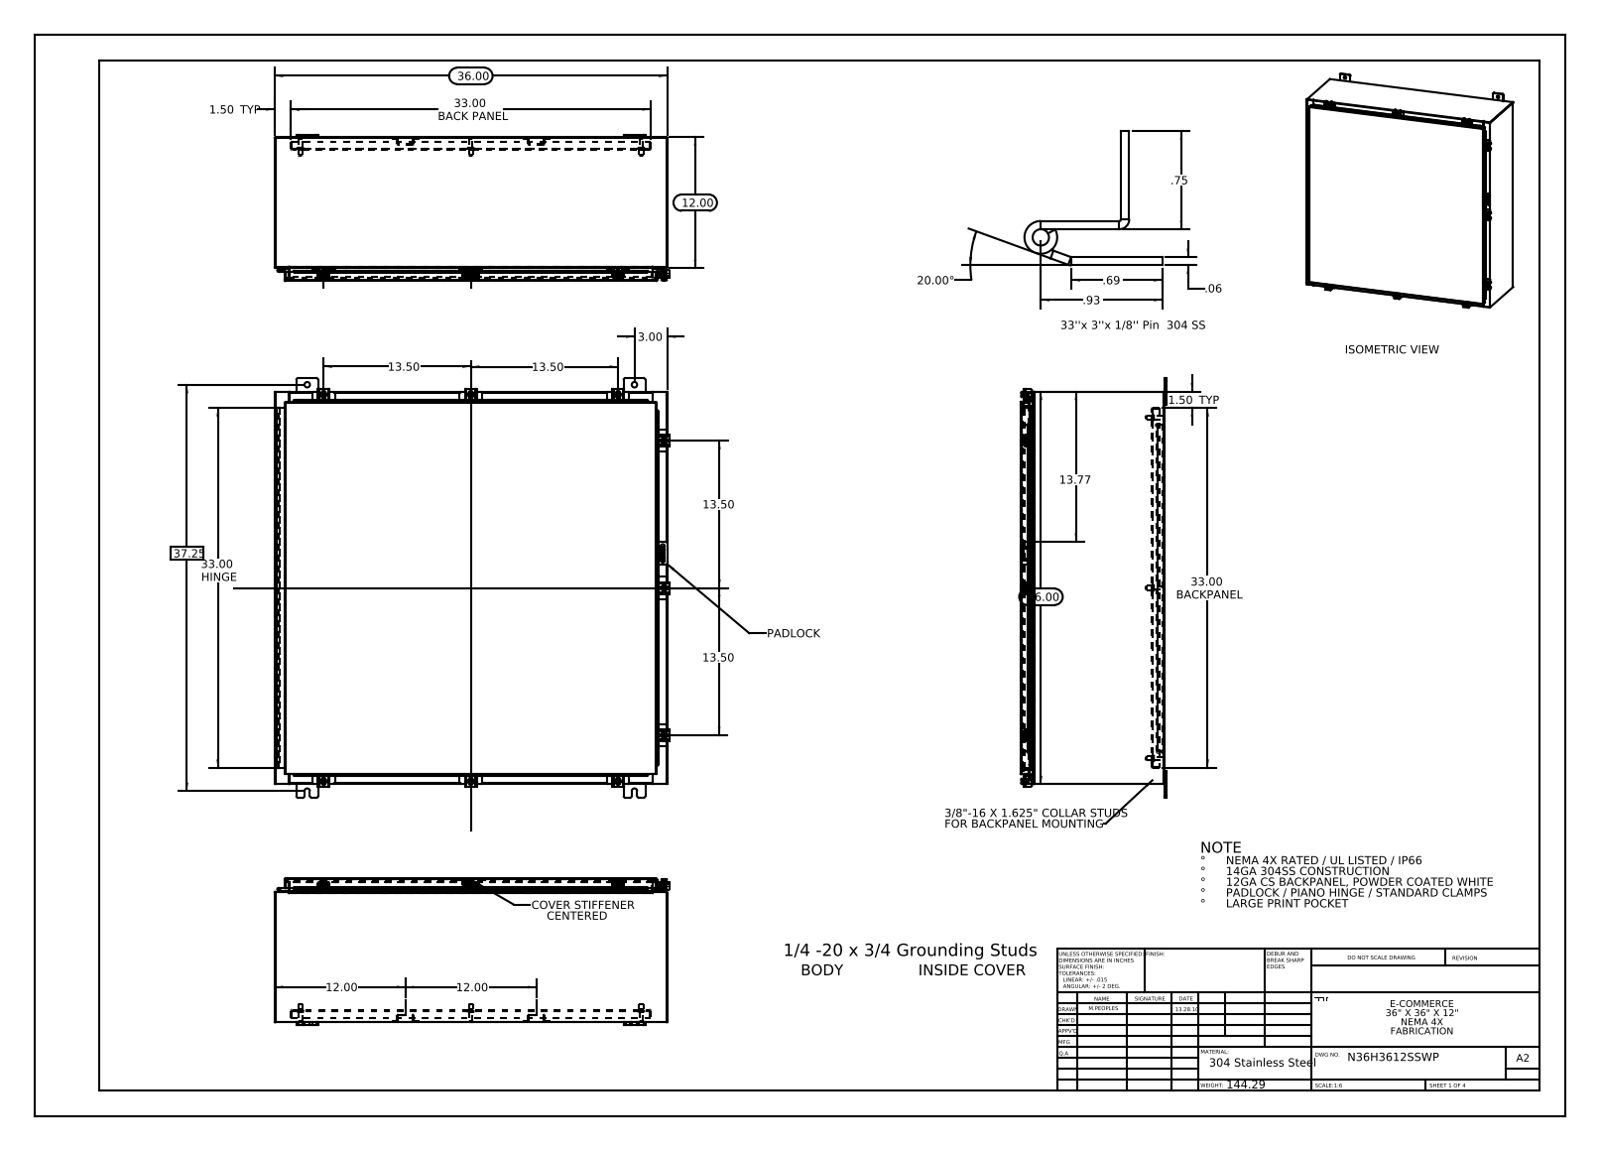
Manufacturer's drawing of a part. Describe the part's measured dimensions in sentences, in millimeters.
The part is named "N36H3612SSWP 125 Pin Hinge; N36H3612SSWP Hinge Enclosure Side2; N36H3612SSWP Body; N36H3612SSWP Padlock Hasp (+8 more)". Its 3-D file was written by "SolidWorks 2013 (CONFIG_CONTROL_DESIGN)". It is 69 solids with 2594 faces: 1358 planar, 1076 cylindrical and 160 other. Overall it measures 977.9 by 919.8 by 340.1 millimeters. Its volume is 8 285 000 cubic millimeters and its surface area 8 172 000 square millimeters. Round holes: 12 of diameter 12.7, 9 of diameter 5.4, 9 of diameter 6.6, 6 of diameter 6.4, 2 of diameter 3.2, 1 of diameter 3.2. Round bosses or shafts: 10 of diameter 6.4, 9 of diameter 12.7, 9 of diameter 10.1, 8 of diameter 15.9, 8 of diameter 9.5, 8 of diameter 8.4. Partial cylindrical surfaces (rounded edges, fillets, slot ends): 42 of radius 1.5, 39 of radius 0.3, 33 of radius 2.2, 24 of radius 4.8, 18 of radius 3, 18 of radius 3.6, 13 of radius 1.3, 12 of radius 2. The main face-to-face distances are 1.9, 333.4, 912.5, 331.5, 335.3, 2.6, 25.4, 308, 27.3, 306.1. The hole center spacings are 342.9, 347, 396.9, 453.4, 600.2, 848.8, 866, 913.9.
